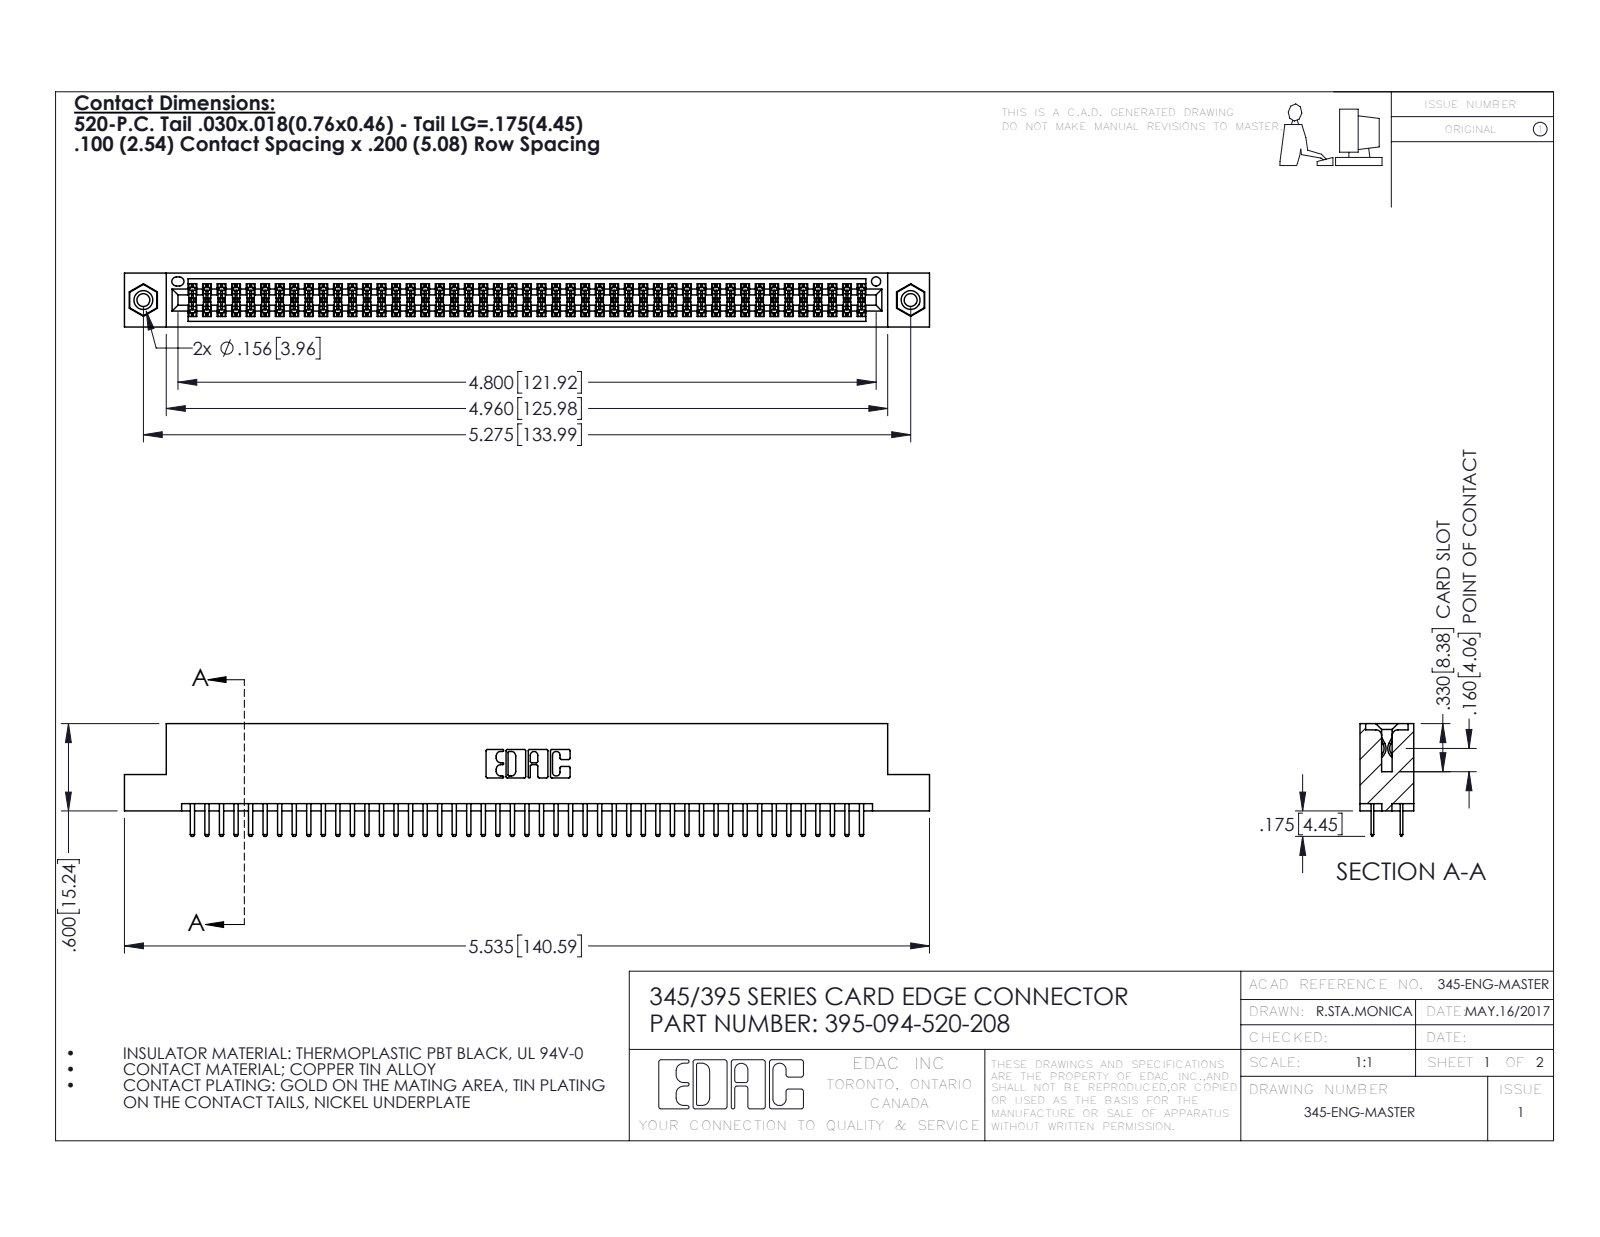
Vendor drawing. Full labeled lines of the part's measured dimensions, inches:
Part name (STEP PRODUCT): 345-292-001_345-293-120; 395-094-520-208; 345 Part_Flush Mounting Lugs - 0.156 Dia-TI; 345-250-001_345-250-003-102
STEP written by: SolidWorks 2016 (CONFIG_CONTROL_DESIGN)
Units: inches
Bodies: 97 solids, 5262 faces (3402 planar, 1844 cylindrical, 16 other)
Overall size (bounding box): 5.535 × 0.775 × 0.37
Volume: 0.833 in³ · Surface area: 31.32 in²
Round holes (diameter × count): ⌀0.089 ×2, ⌀0.125 ×2, ⌀0.156 ×2, ⌀0.064 ×1
Round bosses / shafts (diameter × count): ⌀0.155 ×2
Partial cylindrical surfaces — rounded edges, fillets, slot ends (radius × count): R0.006 ×141, R0.01 ×98, R0.01 ×22, R0.007 ×6, R0.031 ×6, R0.026 ×3, R0.014 ×2, R0.019 ×2
Main face-to-face distances: 0.072, 0.298, 0.2, 0.37, 0.098, 0.272, 0.025, 0.225, 0.022, 0.072
Hole centre spacings: 0.27, 5.039, 5.275
